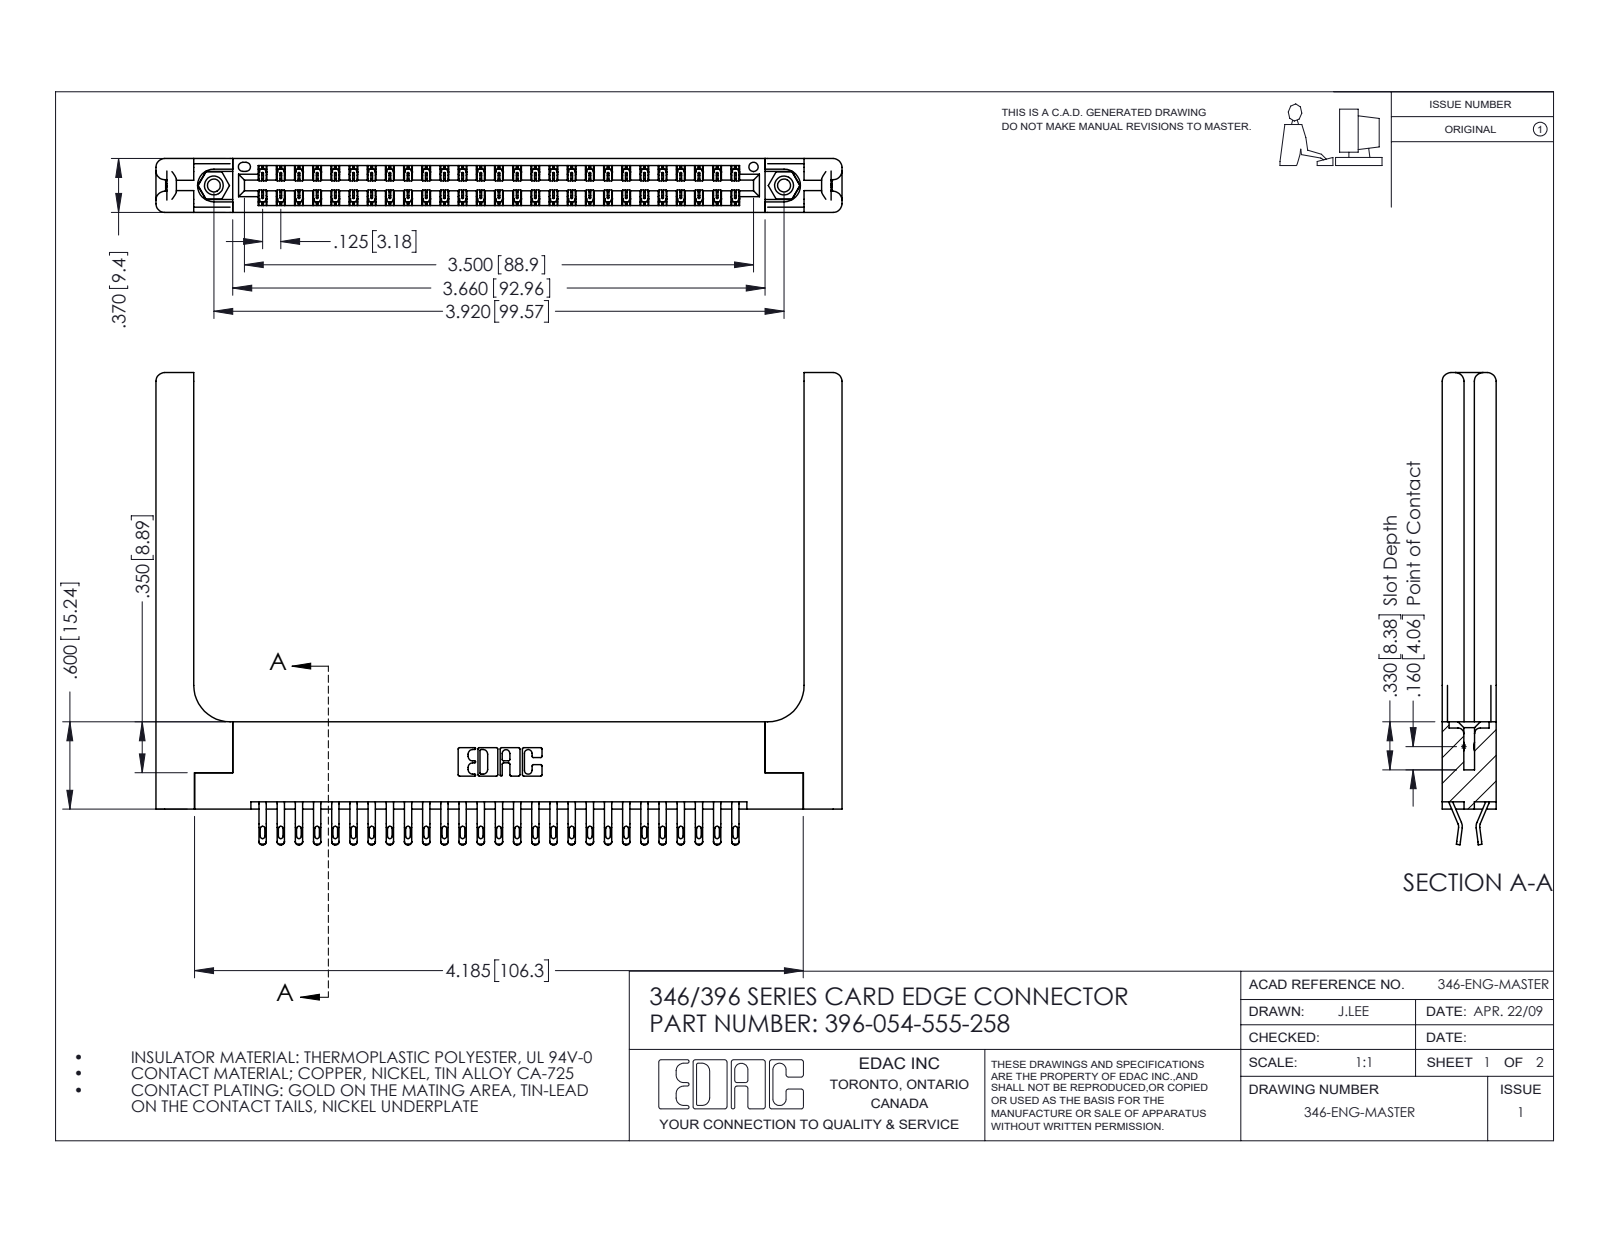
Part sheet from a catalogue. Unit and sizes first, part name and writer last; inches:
Units: inches
Overall size (bounding box): 4.716 × 3.245 × 0.37
Round holes (diameter × count): ⌀0.089 ×2, ⌀0.125 ×2, ⌀0.156 ×2, ⌀0.064 ×1
Round bosses / shafts (diameter × count): ⌀0.155 ×2
Partial cylindrical surfaces — rounded edges, fillets, slot ends (radius × count): R0.016 ×108, R0.02 ×108, R0.006 ×81, R0.01 ×22, R0.06 ×16, R0.007 ×6, R0.031 ×6, R0.026 ×3
Main face-to-face distances: 0.37, 0.072, 0.048, 0.322, 0.148, 0.15, 0.25, 0.025, 0.298, 0.275
Hole centre spacings: 0.246, 3.712, 3.92
Volume: 1.173 in³ · Surface area: 33.18 in²
Bodies: 59 solids, 3510 faces (2006 planar, 1444 cylindrical, 60 other)
Part name (STEP PRODUCT): 345-292-001_555 Tail; 346-220-058_345-220-058; 345-250-001_345-250-001-102; 346 Part_Flush Mounting Lugs - 0.156 Dia-TH (+1 more)
STEP written by: SolidWorks 2016 (CONFIG_CONTROL_DESIGN)
